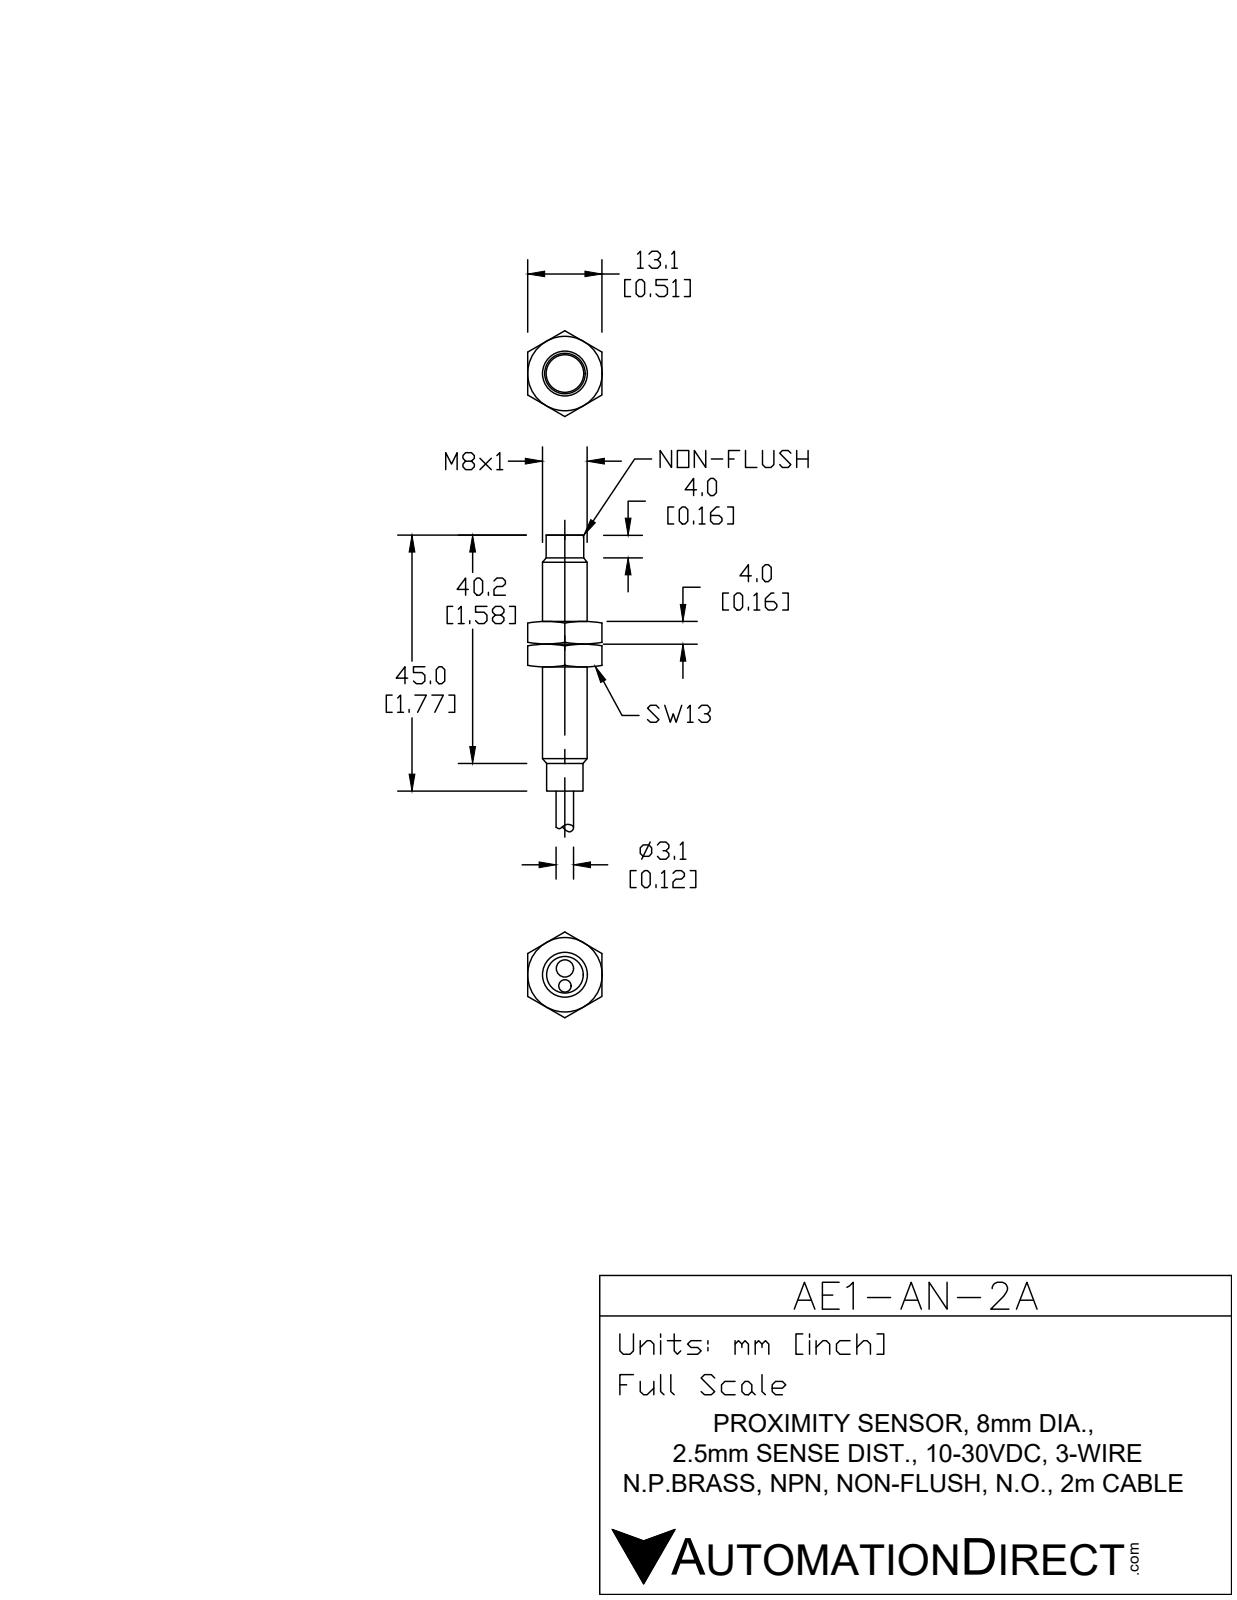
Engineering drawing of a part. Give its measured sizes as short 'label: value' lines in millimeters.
name: AE1-AN-2A
written by: SolidWorks 2017 (AUTOMOTIVE_DESIGN)
unit: mm
bodies: 4 solids, 30 faces (10 planar, 12 cylindrical, 8 other)
size: 82.6 × 8 × 8
volume: 2 380 mm³; area: 1 726 mm²
holes: 1× ⌀3.1, 1× ⌀5.8
bosses: 1× ⌀8, 1× ⌀6.5, 1× ⌀6.5
face distances: 36.2, 4, 40.2, 44.5, 40.5, 4.3, 2.4, 42.6, 38.6, 1.9
hole spacings: 1.1
